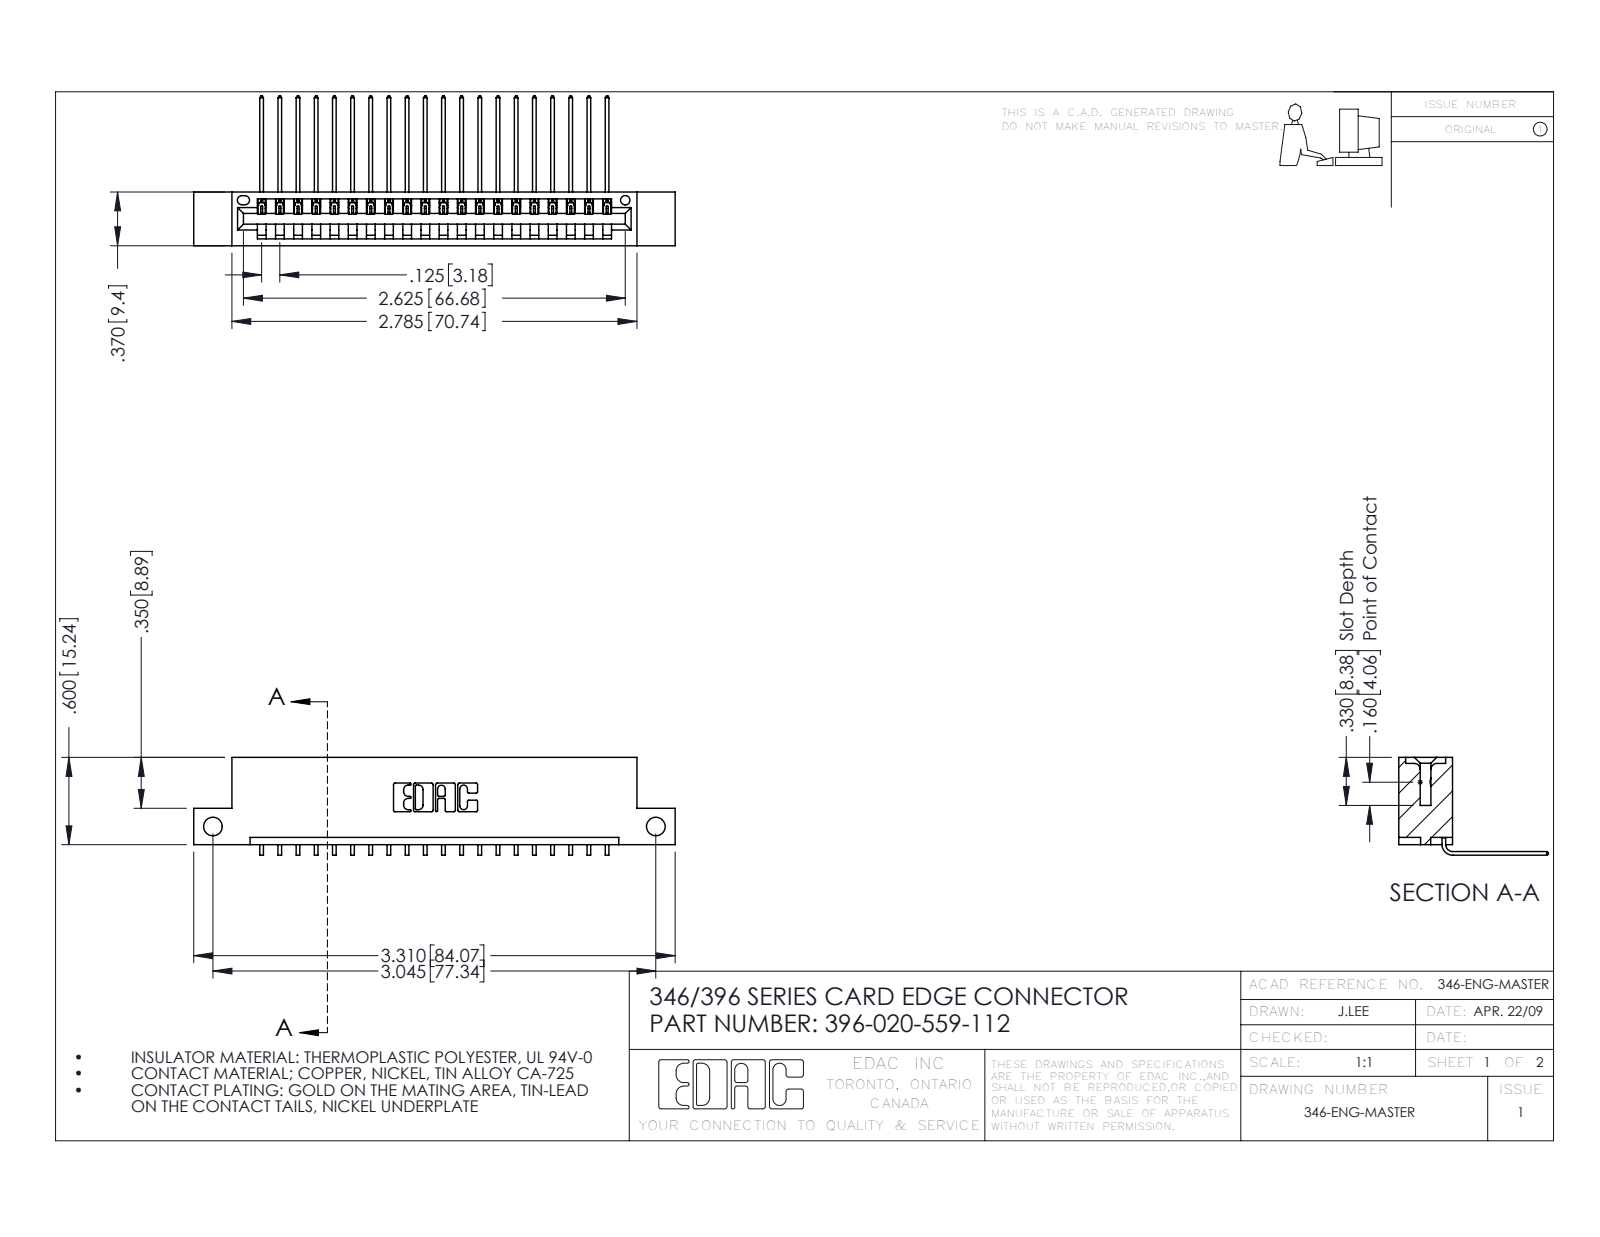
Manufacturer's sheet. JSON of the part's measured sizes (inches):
{"part_name": "346 Part_Flush Mounting Lugs - Side Mount; 345-292-001_558 559 Tail - 1; 396-020-559-112", "step_written_by": "SolidWorks 2016 (CONFIG_CONTROL_DESIGN)", "units": "inches", "bodies": {"solids": 21, "faces": 1322, "planar": 916, "cylindrical": 406, "other": 0}, "overall_size": [3.31, 1.03, 0.673], "volume_in3": 0.481, "surface_area_in2": 15.28, "round_holes": [[0.128, 2], [0.064, 1]], "partial_cylinders_radius": [[0.006, 40], [0.01, 22], [0.007, 6], [0.031, 6], [0.026, 3], [0.031, 2], [0.04, 2], [0.014, 1]], "face_to_face_distances": [0.048, 0.322, 0.37, 0.25, 0.072, 0.025, 0.298, 0.148, 0.222, 0.1], "hole_center_spacings": [3.045]}
